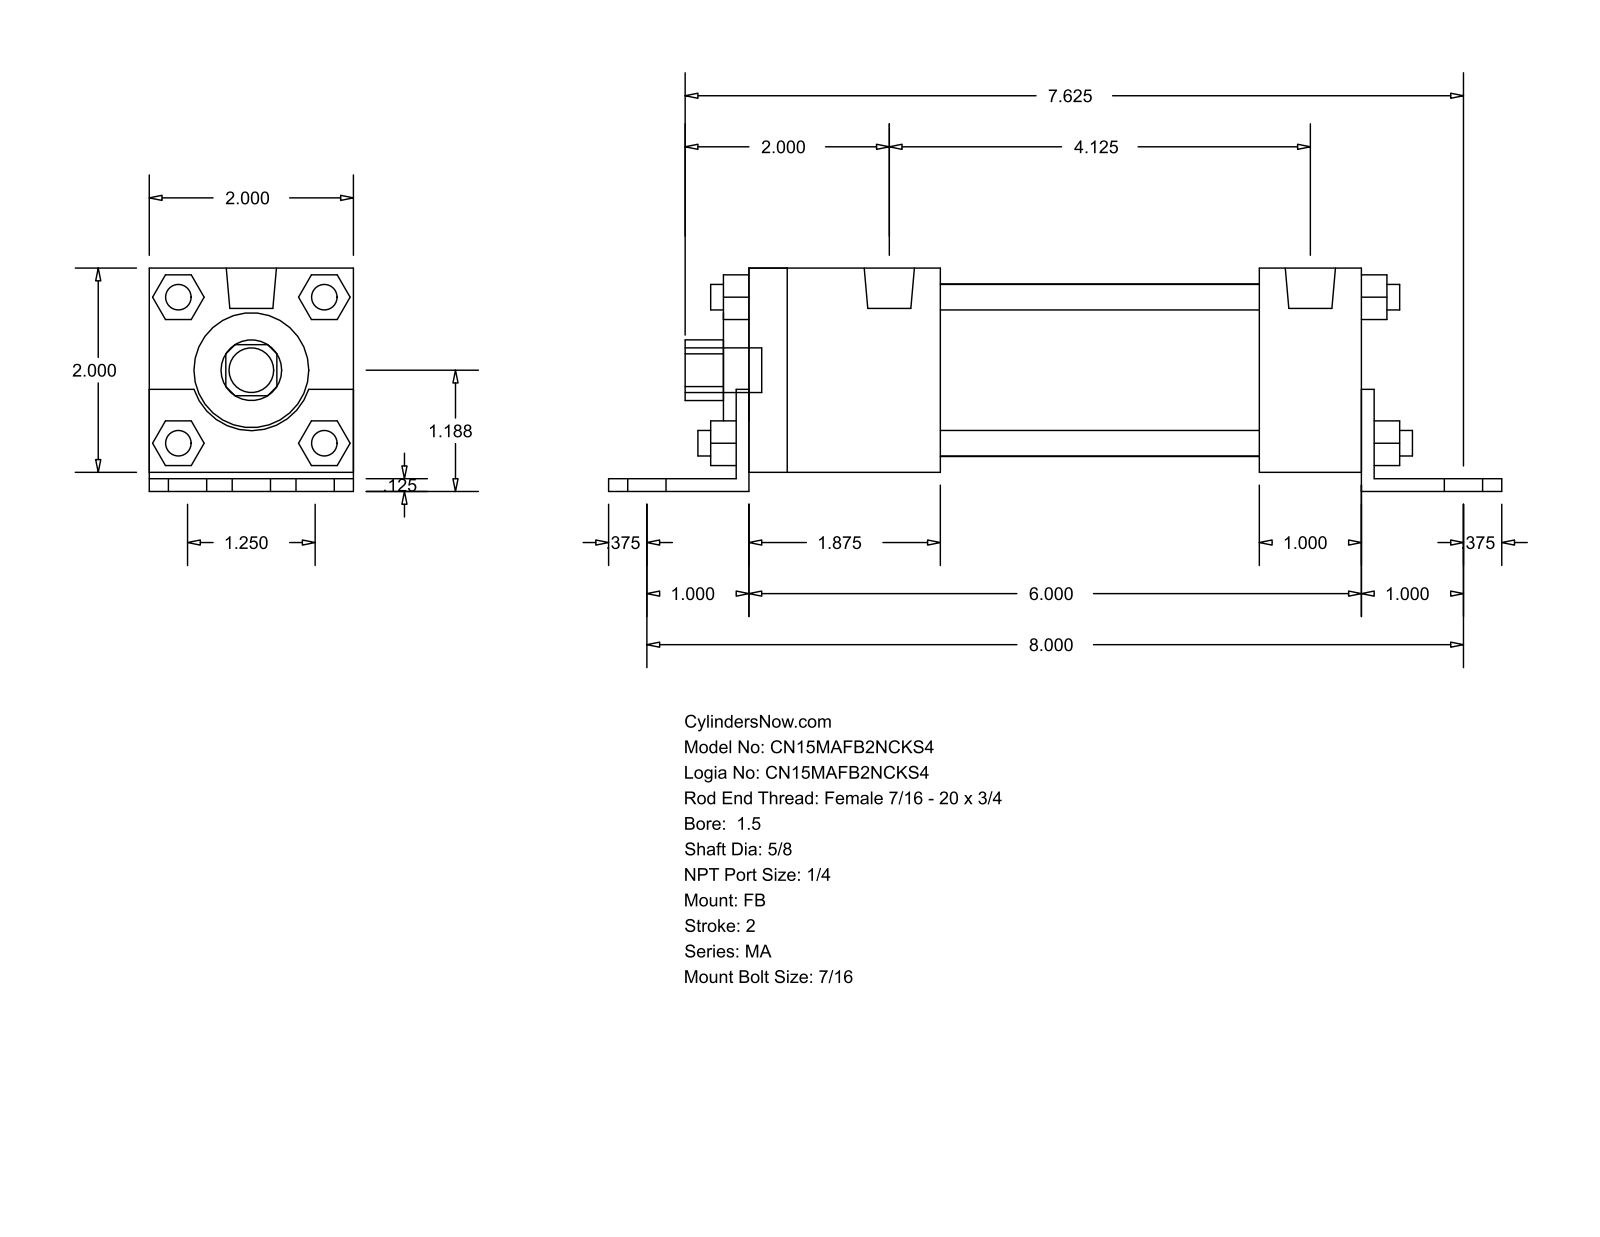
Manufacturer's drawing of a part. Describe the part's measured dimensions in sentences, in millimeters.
The part is named "MA_FB__0150_0.625". Its 3-D file was written by "GSSL Pune (CONFIG_CONTROL_DESIGN)". It is 0 solids with 140 faces: 105 planar, 35 cylindrical and 0 other. Overall it measures 222.25 by 55.56 by 50.8 millimeters. Round holes: 1 of diameter 15.88, 1 of diameter 28.57, 1 of diameter 42.93. Round bosses or shafts: 7 of diameter 11.11, 4 of diameter 7.94, 4 of diameter 6.35, 2 of diameter 12.49. Partial cylindrical surfaces (rounded edges, fillets, slot ends): 1 of radius 7.54, 1 of radius 15.05. The main face-to-face distances are 50.8, 3.17, 4.76, 55.56, 1.59, 52.39, 25.4, 158.75, 6.35, 152.4.
